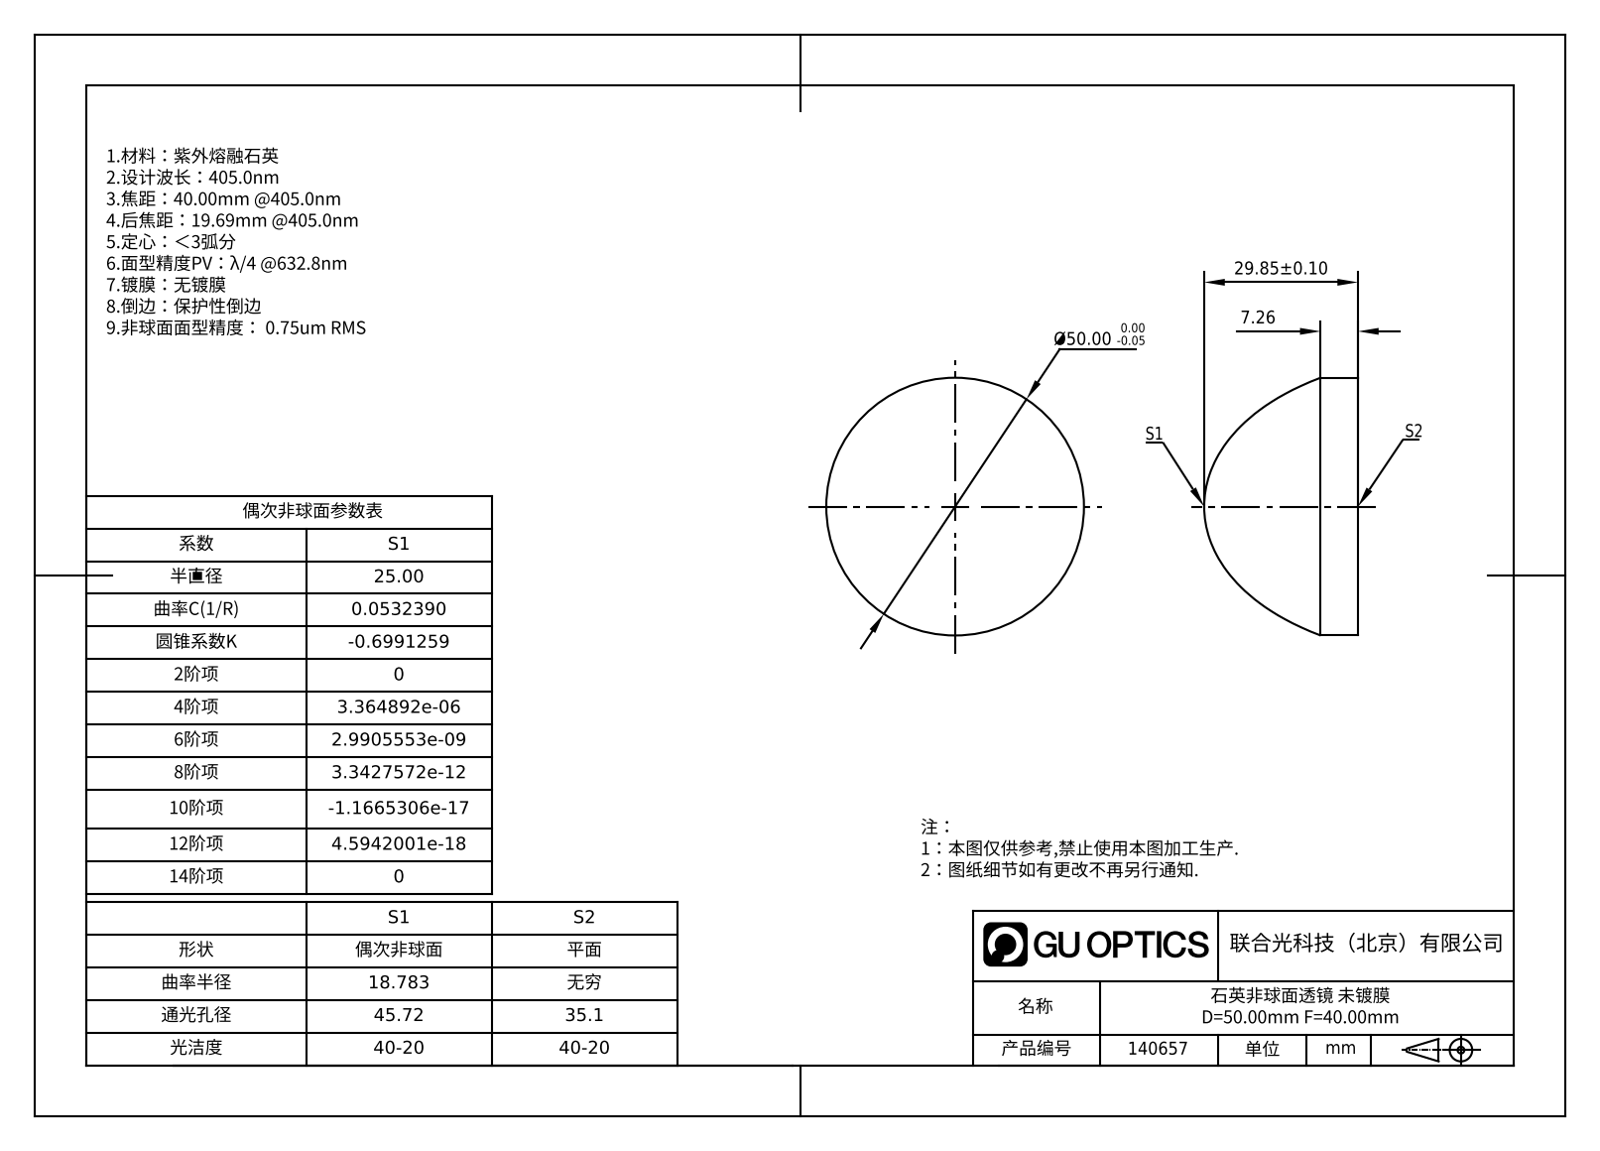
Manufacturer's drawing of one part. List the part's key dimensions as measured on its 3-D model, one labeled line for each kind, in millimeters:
Part name (STEP PRODUCT): surfaces 1,2.stp; GASP21-050-040; GASP21-050-040.stp
STEP written by: SolidWorks 2023 (CONFIG_CONTROL_DESIGN)
Units: millimetres
Bodies: 1 solid, 5 faces (1 planar, 2 cylindrical, 2 other)
Overall size (bounding box): 50 × 50 × 29.85
Volume: 38 926 mm³ · Surface area: 6 406 mm²
Round bosses / shafts (diameter × count): ⌀50 ×1
